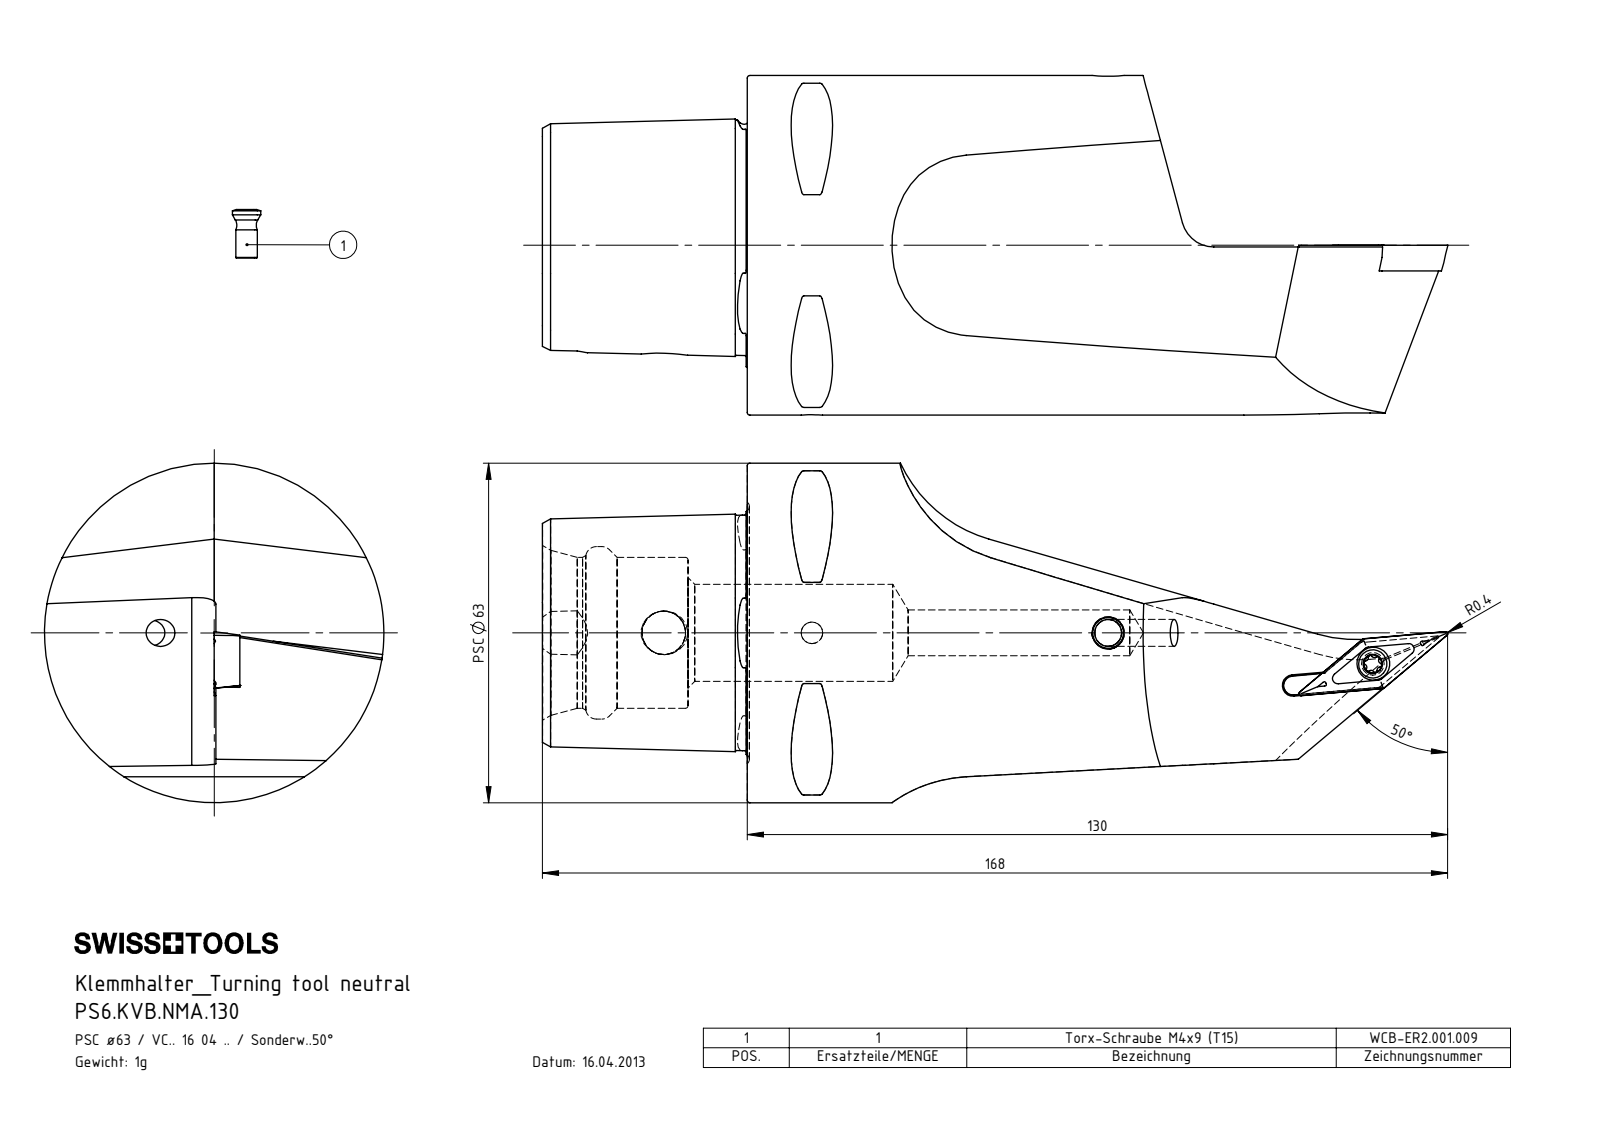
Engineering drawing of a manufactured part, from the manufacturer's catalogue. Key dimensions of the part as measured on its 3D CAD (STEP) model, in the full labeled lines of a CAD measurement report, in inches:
Part name (STEP PRODUCT): WCB-ER2.001.009_A; PS6-KVB.NMA.130_A; VCMT160404; KVT_MB_600_060 (+1 more)
STEP written by: SolidWorks 2017 (AUTOMOTIVE_DESIGN)
Units: inches
Bodies: 5 solids, 278 faces (55 planar, 72 cylindrical, 151 other)
Overall size (bounding box): 6.615 × 2.48 × 2.48
Volume: 15.08 in³ · Surface area: 56.1 in²
Round holes (diameter × count): ⌀0.197 ×2, ⌀0.13 ×1, ⌀0.157 ×1, ⌀0.173 ×1, ⌀0.24 ×1, ⌀0.319 ×1, ⌀0.335 ×1, ⌀0.709 ×1, ⌀1.102 ×1, ⌀1.26 ×1
Round bosses / shafts (diameter × count): ⌀2.48 ×1, ⌀0.236 ×1, ⌀0.207 ×1, ⌀0.157 ×1
Partial cylindrical surfaces — rounded edges, fillets, slot ends (radius × count): R0.02 ×8, R0.013 ×6, R0.023 ×6, R1.024 ×4, R0.236 ×2, R0.069 ×1
Main face-to-face distances: 1.496, 0.98, 1.063, 0.433, 0.176, 2.197, 1.488, 0.425, 0.187, 1.14
Hole centre spacings: 1.083, 1.947, 1.951, 2.165, 3.248, 4.106, 4.11, 5.187
